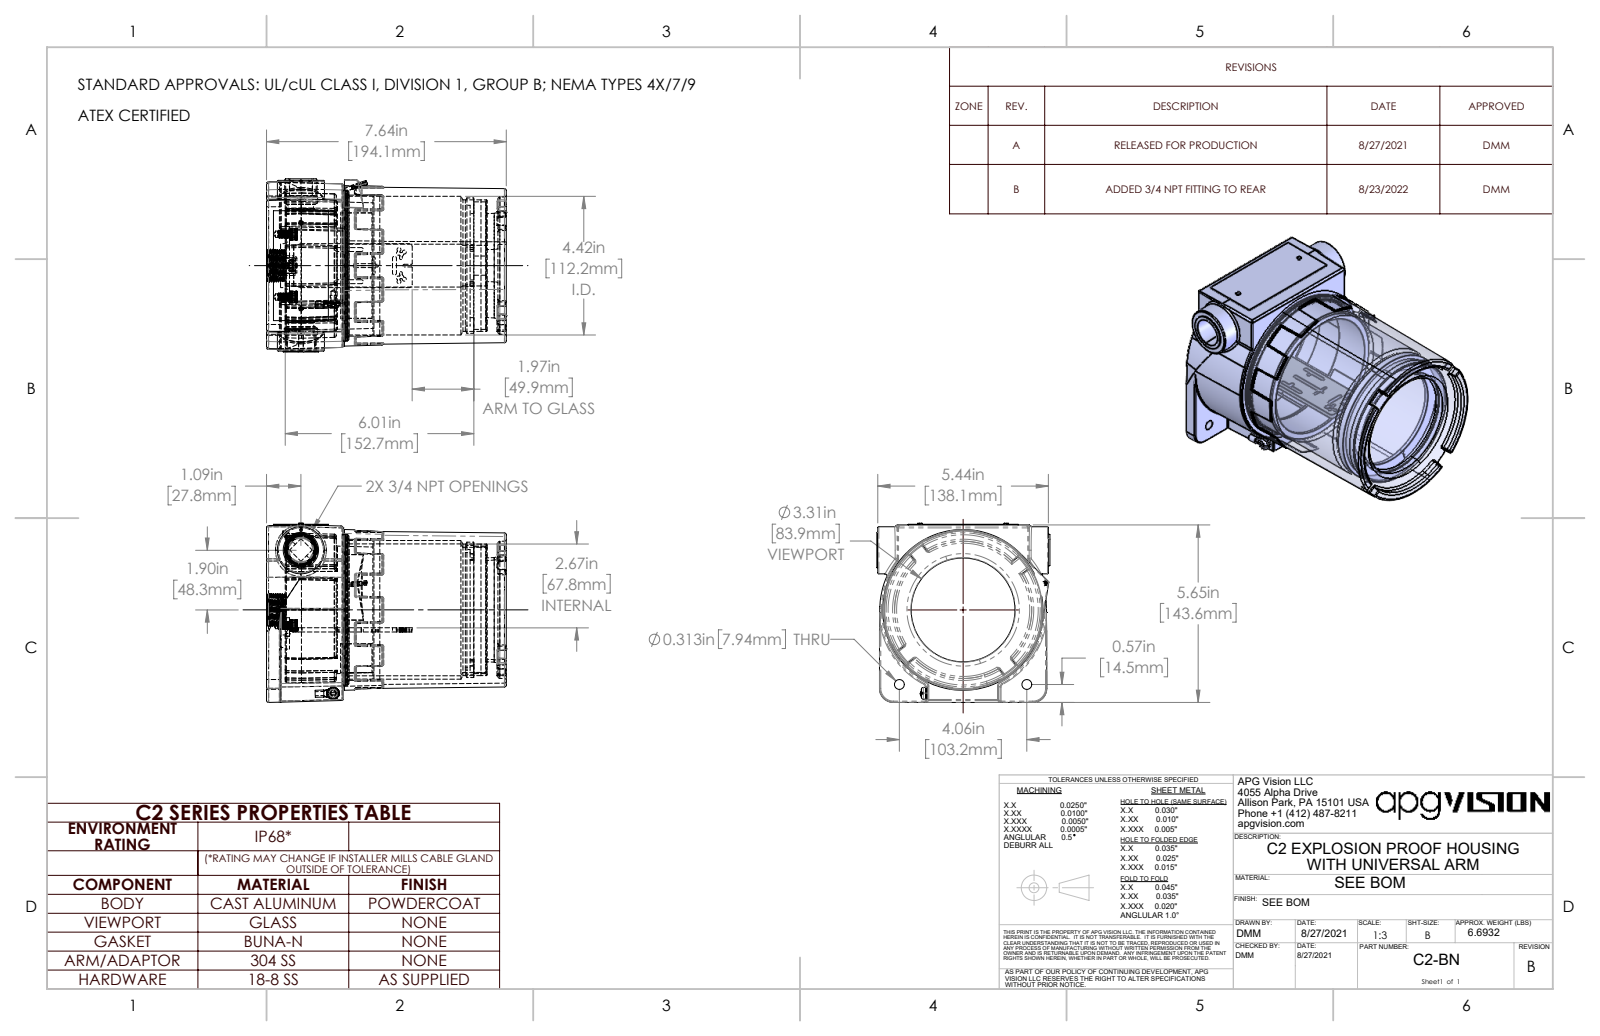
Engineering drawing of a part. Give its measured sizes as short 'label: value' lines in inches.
name: 92196A535_92196A535; 4638K515_4638K515; C2-BN; 201109 (+1 more)
written by: SolidWorks 2021 (CONFIG_CONTROL_DESIGN)
unit: in
bodies: 20 solids, 1526 faces (478 planar, 252 cylindrical, 796 other)
size: 7.643 × 5.71 × 5.519
volume: 66.08 in³; area: 458.6 in²
holes: 2× ⌀0.067, 2× ⌀0.094, 2× ⌀0.145, 2× ⌀0.188, 2× ⌀0.201, 2× ⌀0.25, 2× ⌀0.313, 2× ⌀0.4, 1× ⌀0.107, 1× ⌀0.129, 1× ⌀0.195, 1× ⌀0.197
bosses: 2× ⌀0.19, 2× ⌀0.185, 2× ⌀0.073, 1× ⌀4.77, 1× ⌀4.492, 1× ⌀4.312, 1× ⌀4.062, 1× ⌀1.5
rounds: 38× R0.02, 24× R0.062, 19× R0.031, 11× R0.031, 6× R0.042, 6× R0.25, 5× R0.063, 5× R0.063
face distances: 0.594, 6.982, 6.388, 6.607, 6.013, 0.375, 0.02, 0.135, 2.437, 1.844
hole spacings: 1.118, 0.707, 1.581, 1.781, 2.058, 2.14, 2.88, 3.125
